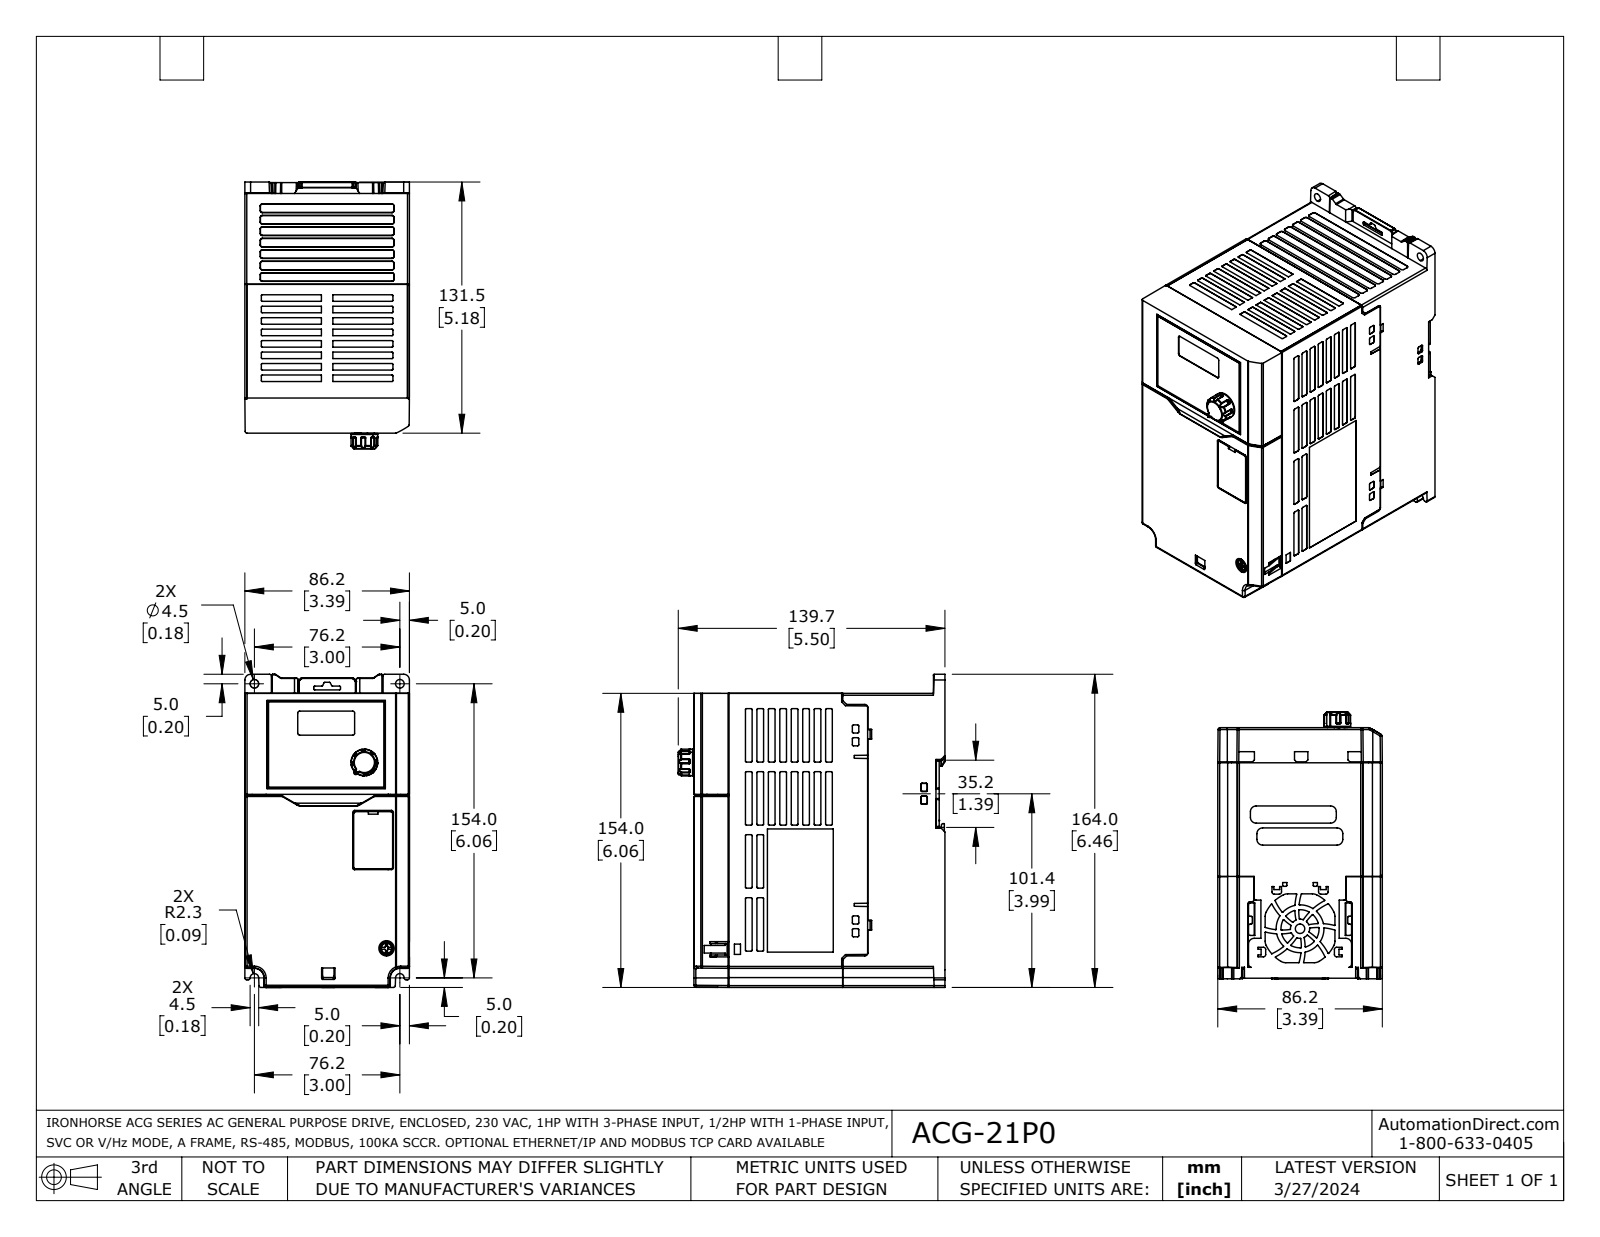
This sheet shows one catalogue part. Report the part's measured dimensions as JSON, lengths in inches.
{"part_name": "ACG-21P0", "step_written_by": "SolidWorks 2021 (AUTOMOTIVE_DESIGN)", "units": "inches", "bodies": {"solids": 6, "faces": 4492, "planar": 1868, "cylindrical": 1308, "other": 1316}, "overall_size": [6.457, 5.5, 3.394], "volume_in3": 101.9, "surface_area_in2": 197.5, "round_holes": [[0.039, 1], [0.276, 1], [0.472, 1]], "round_bosses_or_shafts": [[0.551, 1], [0.543, 1], [0.236, 1]], "partial_cylinders_radius": [[0.008, 343], [0.02, 288], [0.039, 85], [0.018, 46], [0.012, 27], [0.031, 17], [0.023, 16], [0.118, 12]], "face_to_face_distances": [3.394, 5.059, 3.392, 5.047, 6.063, 6.061, 5.165, 0.106, 3.39, 6.061], "hole_center_spacings": [0.276, 3.675, 3.858]}
